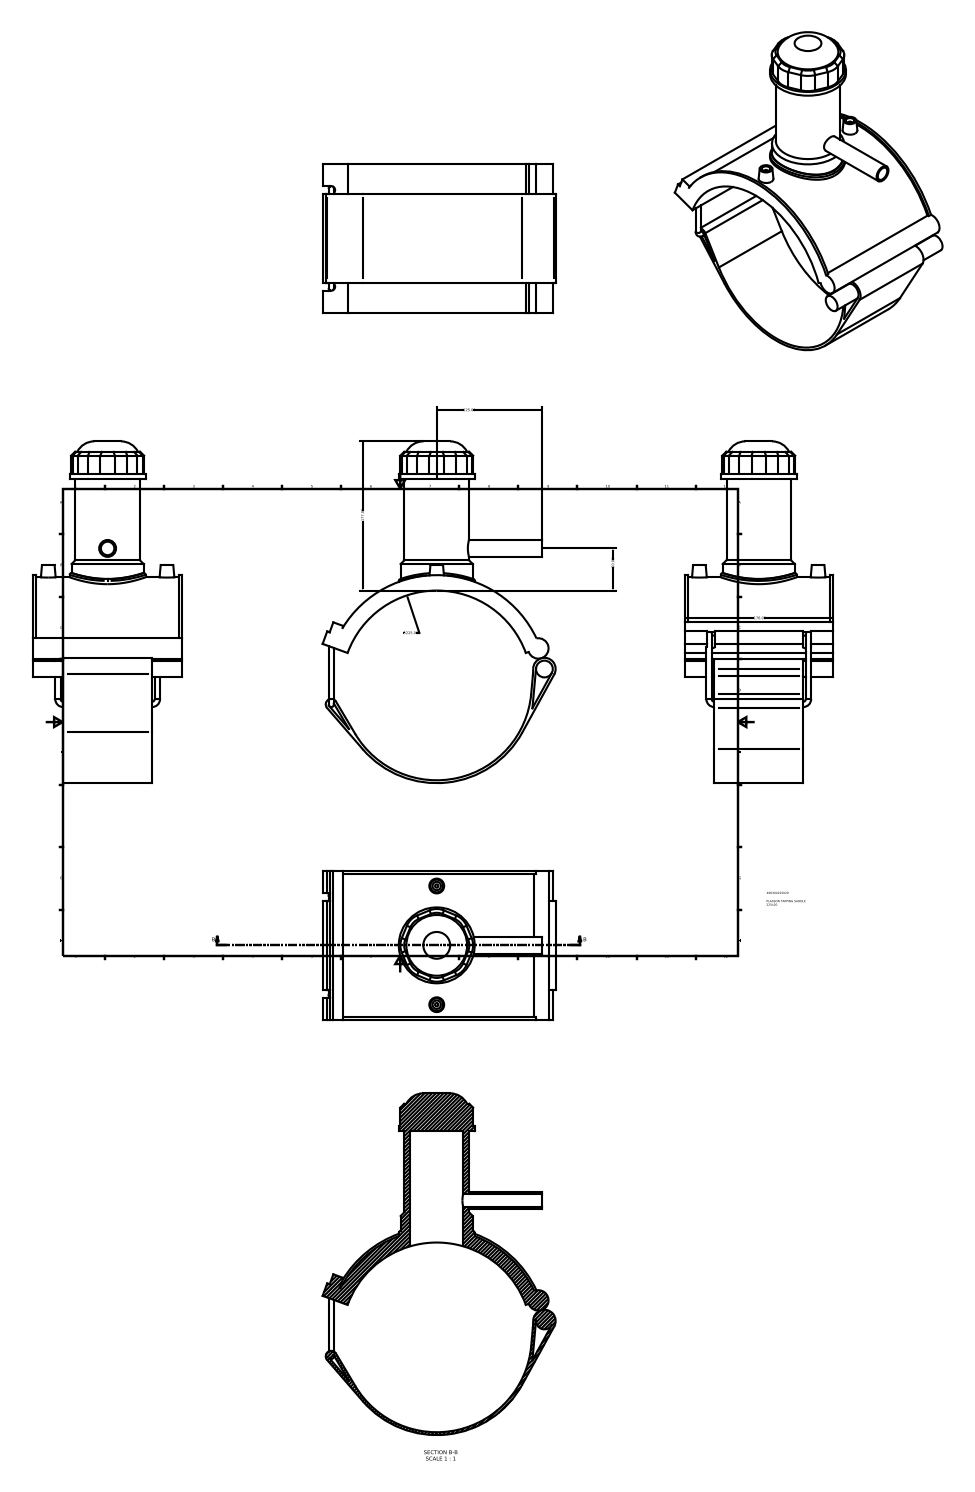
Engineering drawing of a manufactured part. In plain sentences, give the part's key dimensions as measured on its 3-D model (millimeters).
The part is named "496304225020". Its 3-D file was written by "Autodesk Inventor 2015 (AUTOMOTIVE_DESIGN)". It is 1 solid with 121 faces: 68 planar, 38 cylindrical and 15 other. Overall it measures 405.38 by 276.37 by 176 millimeters. Its volume is 1 585 000 cubic millimeters and its surface area 336 705 square millimeters. Round holes: 2 of diameter 10, 1 of diameter 16, 1 of diameter 63. Round bosses or shafts: 2 of diameter 6.3, 2 of diameter 4, 1 of diameter 90, 1 of diameter 85.5, 1 of diameter 76.5, 1 of diameter 20, 1 of diameter 19.9. Partial cylindrical surfaces (rounded edges, fillets, slot ends): 8 of radius 22.5, 2 of radius 4.72, 2 of radius 112.5, 1 of radius 3.15, 1 of radius 6.53, 1 of radius 12.12, 1 of radius 13.33, 1 of radius 115.88. The main face-to-face distances are 176, 3.4, 3.38, 3.37, 35.2, 140.8, 3, 3.15, 28.35, 15.76. The hole center spacings are 70.4, 140.8.
